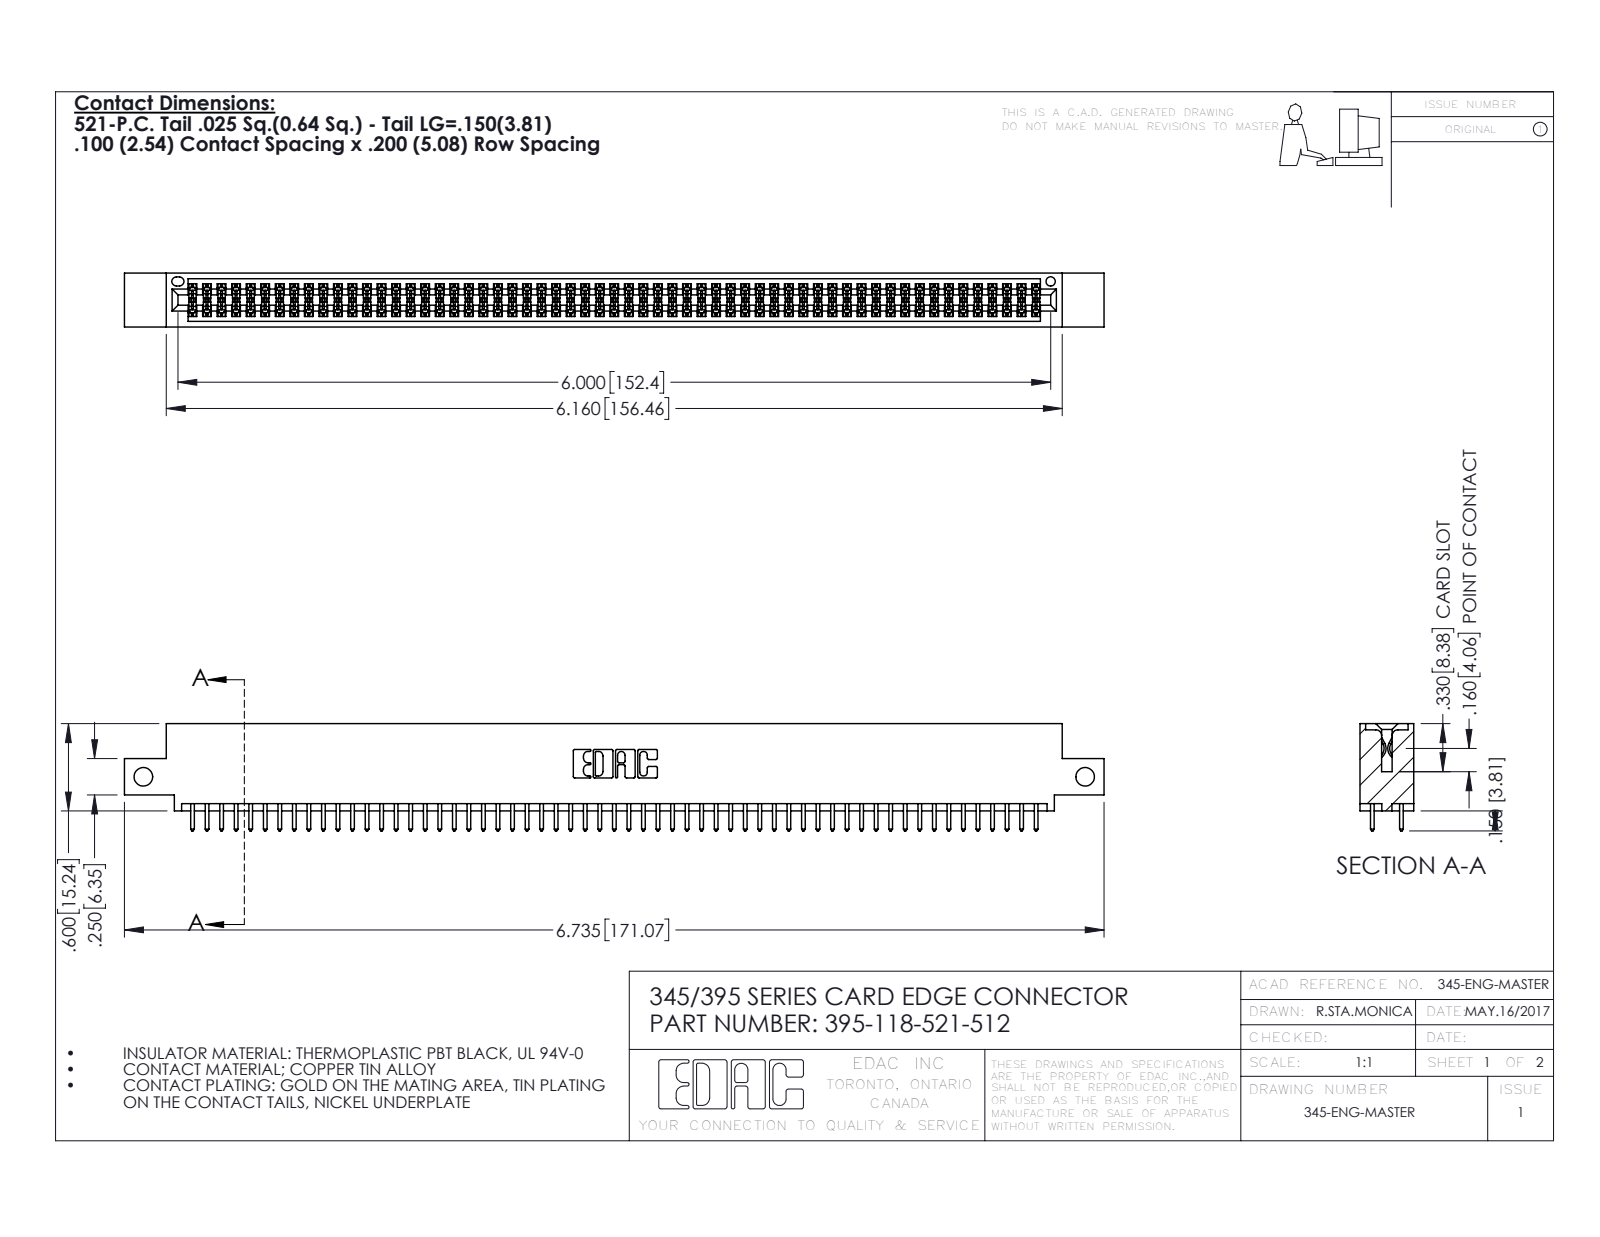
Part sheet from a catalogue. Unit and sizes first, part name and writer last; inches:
Units: inches
Overall size (bounding box): 6.735 × 0.737 × 0.37
Round holes (diameter × count): ⌀0.128 ×2, ⌀0.064 ×1
Partial cylindrical surfaces — rounded edges, fillets, slot ends (radius × count): R0.006 ×177, R0.01 ×118, R0.01 ×22, R0.007 ×6, R0.031 ×6, R0.026 ×3, R0.014 ×2, R0.019 ×2
Main face-to-face distances: 0.298, 0.072, 0.2, 0.098, 0.272, 0.025, 0.37, 0.225, 0.175, 0.149
Hole centre spacings: 6.475
Volume: 1.011 in³ · Surface area: 37.92 in²
Bodies: 119 solids, 6030 faces (3978 planar, 2052 cylindrical, 0 other)
Part name (STEP PRODUCT): 345 Part_0.110 Offset - Side Mount; 395-118-521-512; 345-292-001_345-293-121
STEP written by: SolidWorks 2016 (CONFIG_CONTROL_DESIGN)
